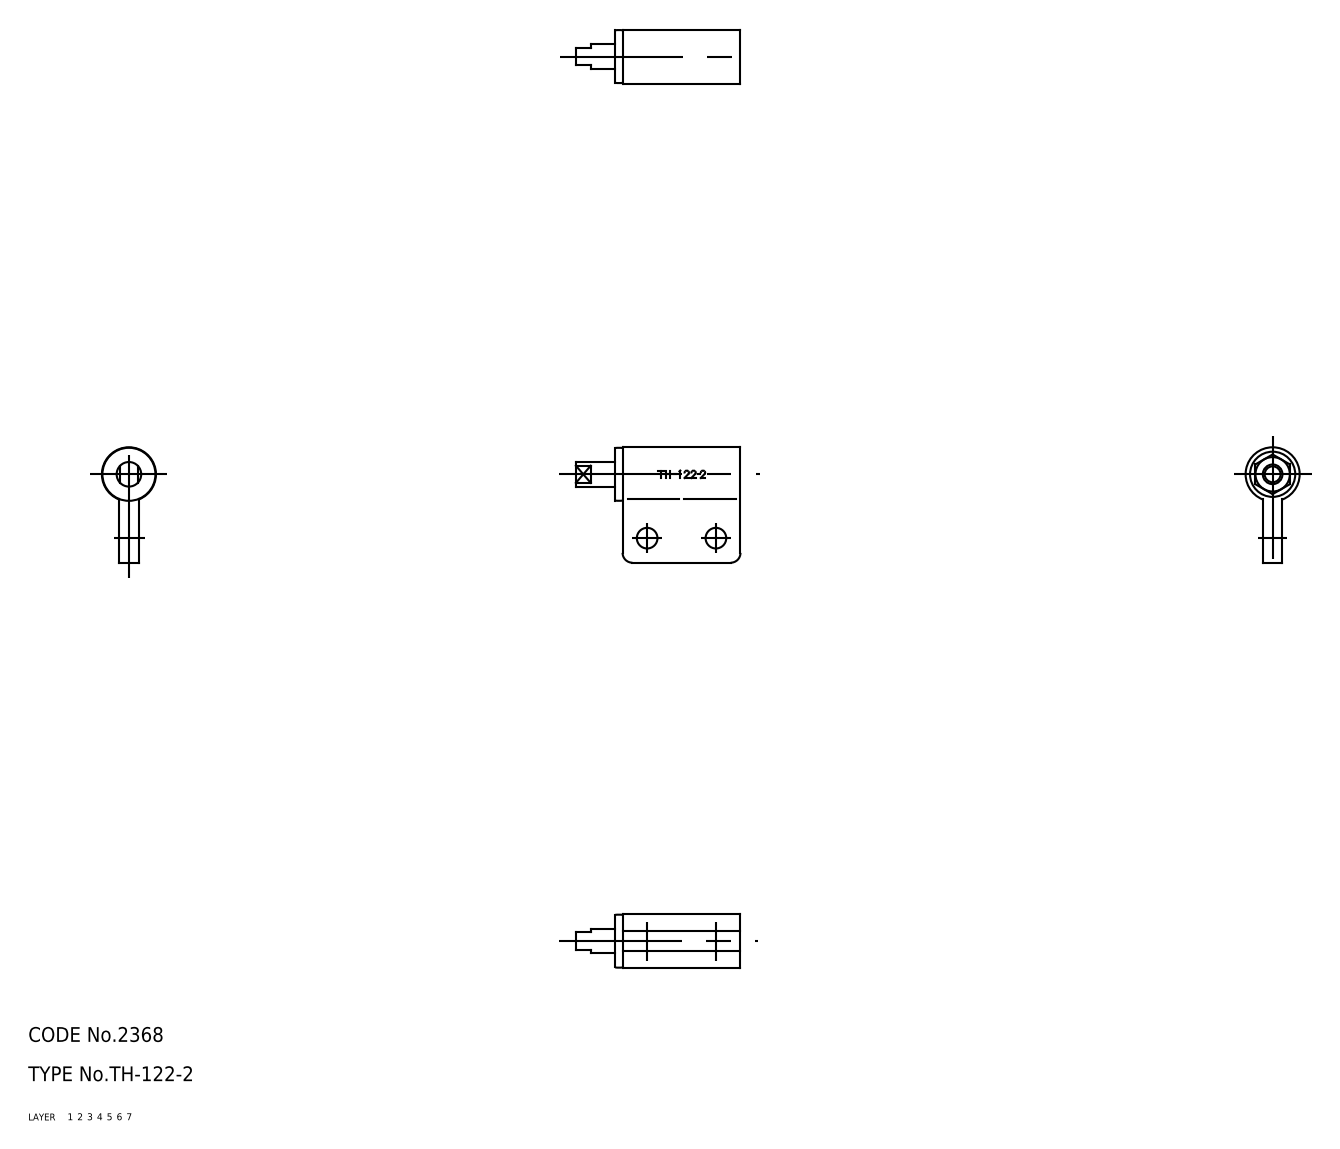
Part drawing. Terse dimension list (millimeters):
name: washer; socket; shaft; nut (+2 more)
written by: CADfix (AUTOMOTIVE_DESIGN)
unit: mm
bodies: 5 solids, 63 faces (0 planar, 0 cylindrical, 63 other)
size: 33.5 × 23.5 × 11
volume: 2 988 mm³; area: 4 262 mm²
